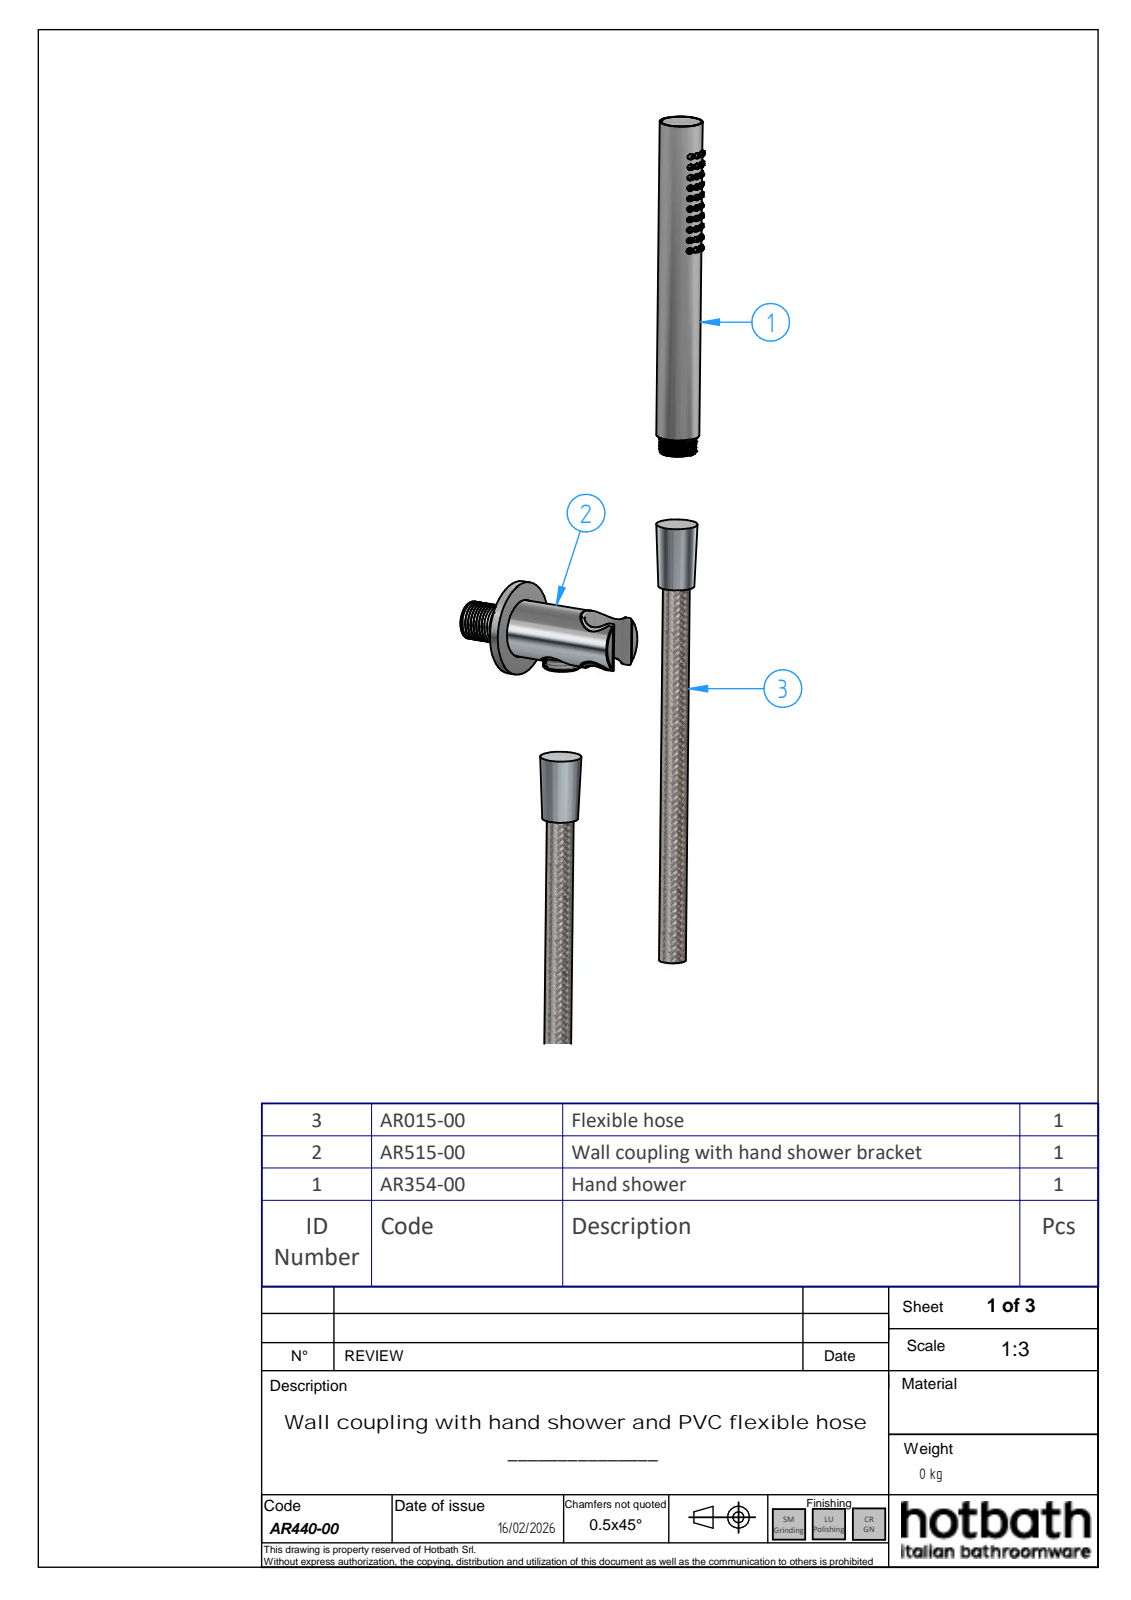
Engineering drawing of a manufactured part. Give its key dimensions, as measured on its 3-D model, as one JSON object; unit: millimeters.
{"part_name": "AR440-00; AR015-00; AR515-00 r1_oa_0; AR517-06 (+8 more)", "step_written_by": "Solid Edge (AUTOMOTIVE_DESIGN)", "units": "millimeters", "bodies": {"solids": 14, "faces": 796, "planar": 171, "cylindrical": 199, "other": 426}, "overall_size": [458.06, 72.15, 52], "volume_mm3": 158452, "surface_area_mm2": 86469, "round_holes": [[3.2, 40], [16.5, 2], [19, 2], [2.36, 1], [3.24, 1], [4.13, 1], [5.68, 1], [8, 1], [8.7, 1], [10, 1], [12.77, 1], [14.4, 1]], "round_bosses_or_shafts": [[15, 2], [52, 1], [39, 1], [31.7, 1], [30, 1], [24, 1], [21.8, 1], [20.95, 1]], "partial_cylinders_radius": [[0.5, 14], [0.35, 4], [0.59, 3], [0.76, 3], [0.22, 2], [0.23, 2], [0.28, 2], [0.65, 2]], "face_to_face_distances": [1.4, 26.7, 57.8, 2.2, 59.2, 5, 2.8, 62.8, 60.6, 61.4], "hole_center_spacings": [7.21, 6, 12, 12.65, 18.44, 4, 18, 24.33]}
